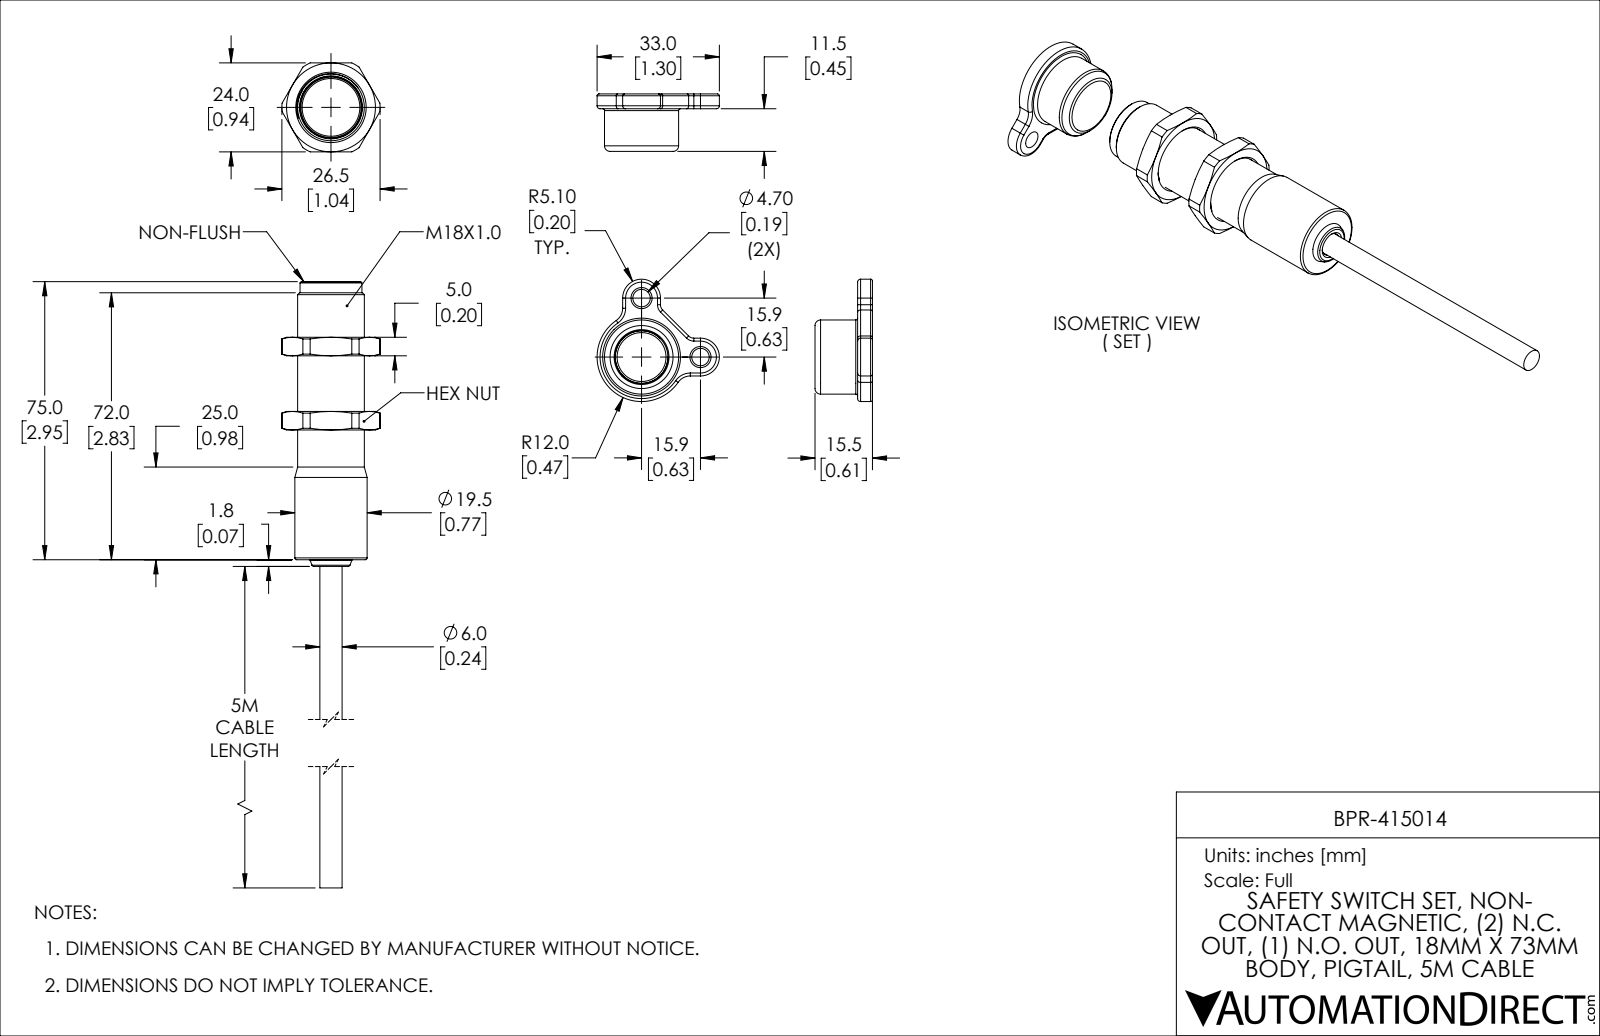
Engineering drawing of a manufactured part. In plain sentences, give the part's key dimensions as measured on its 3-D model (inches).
The part is named "415-BPR". Its 3-D file was written by "SolidWorks 2019 (AUTOMOTIVE_DESIGN)". It is 4 solids with 147 faces: 41 planar, 41 cylindrical and 65 other. Overall it measures 7.224 by 1.287 by 1.116 inches. Its volume is 1.727 cubic inches and its surface area 20.18 square inches. Round holes: 4 of diameter 0.098, 2 of diameter 0.185, 1 of diameter 0.079, 1 of diameter 0.252, 1 of diameter 0.528, 1 of diameter 0.63, 1 of diameter 0.709. Round bosses or shafts: 1 of diameter 0.776, 1 of diameter 0.768, 1 of diameter 0.657, 1 of diameter 0.622, 1 of diameter 0.236. Partial cylindrical surfaces (rounded edges, fillets, slot ends): 5 of radius 0.031, 2 of radius 0.079, 2 of radius 0.157, 2 of radius 0.201, 1 of radius 0.472, 1 of radius 0.522. The main face-to-face distances are 0.591, 1.378, 0.787, 2.165, 1.575, 0.197, 0.945, 0.059, 0.539, 0.984. The hole center spacings are 0.191, 0.481, 0.217, 0.626, 0.68, 0.698, 0.871, 0.509.
